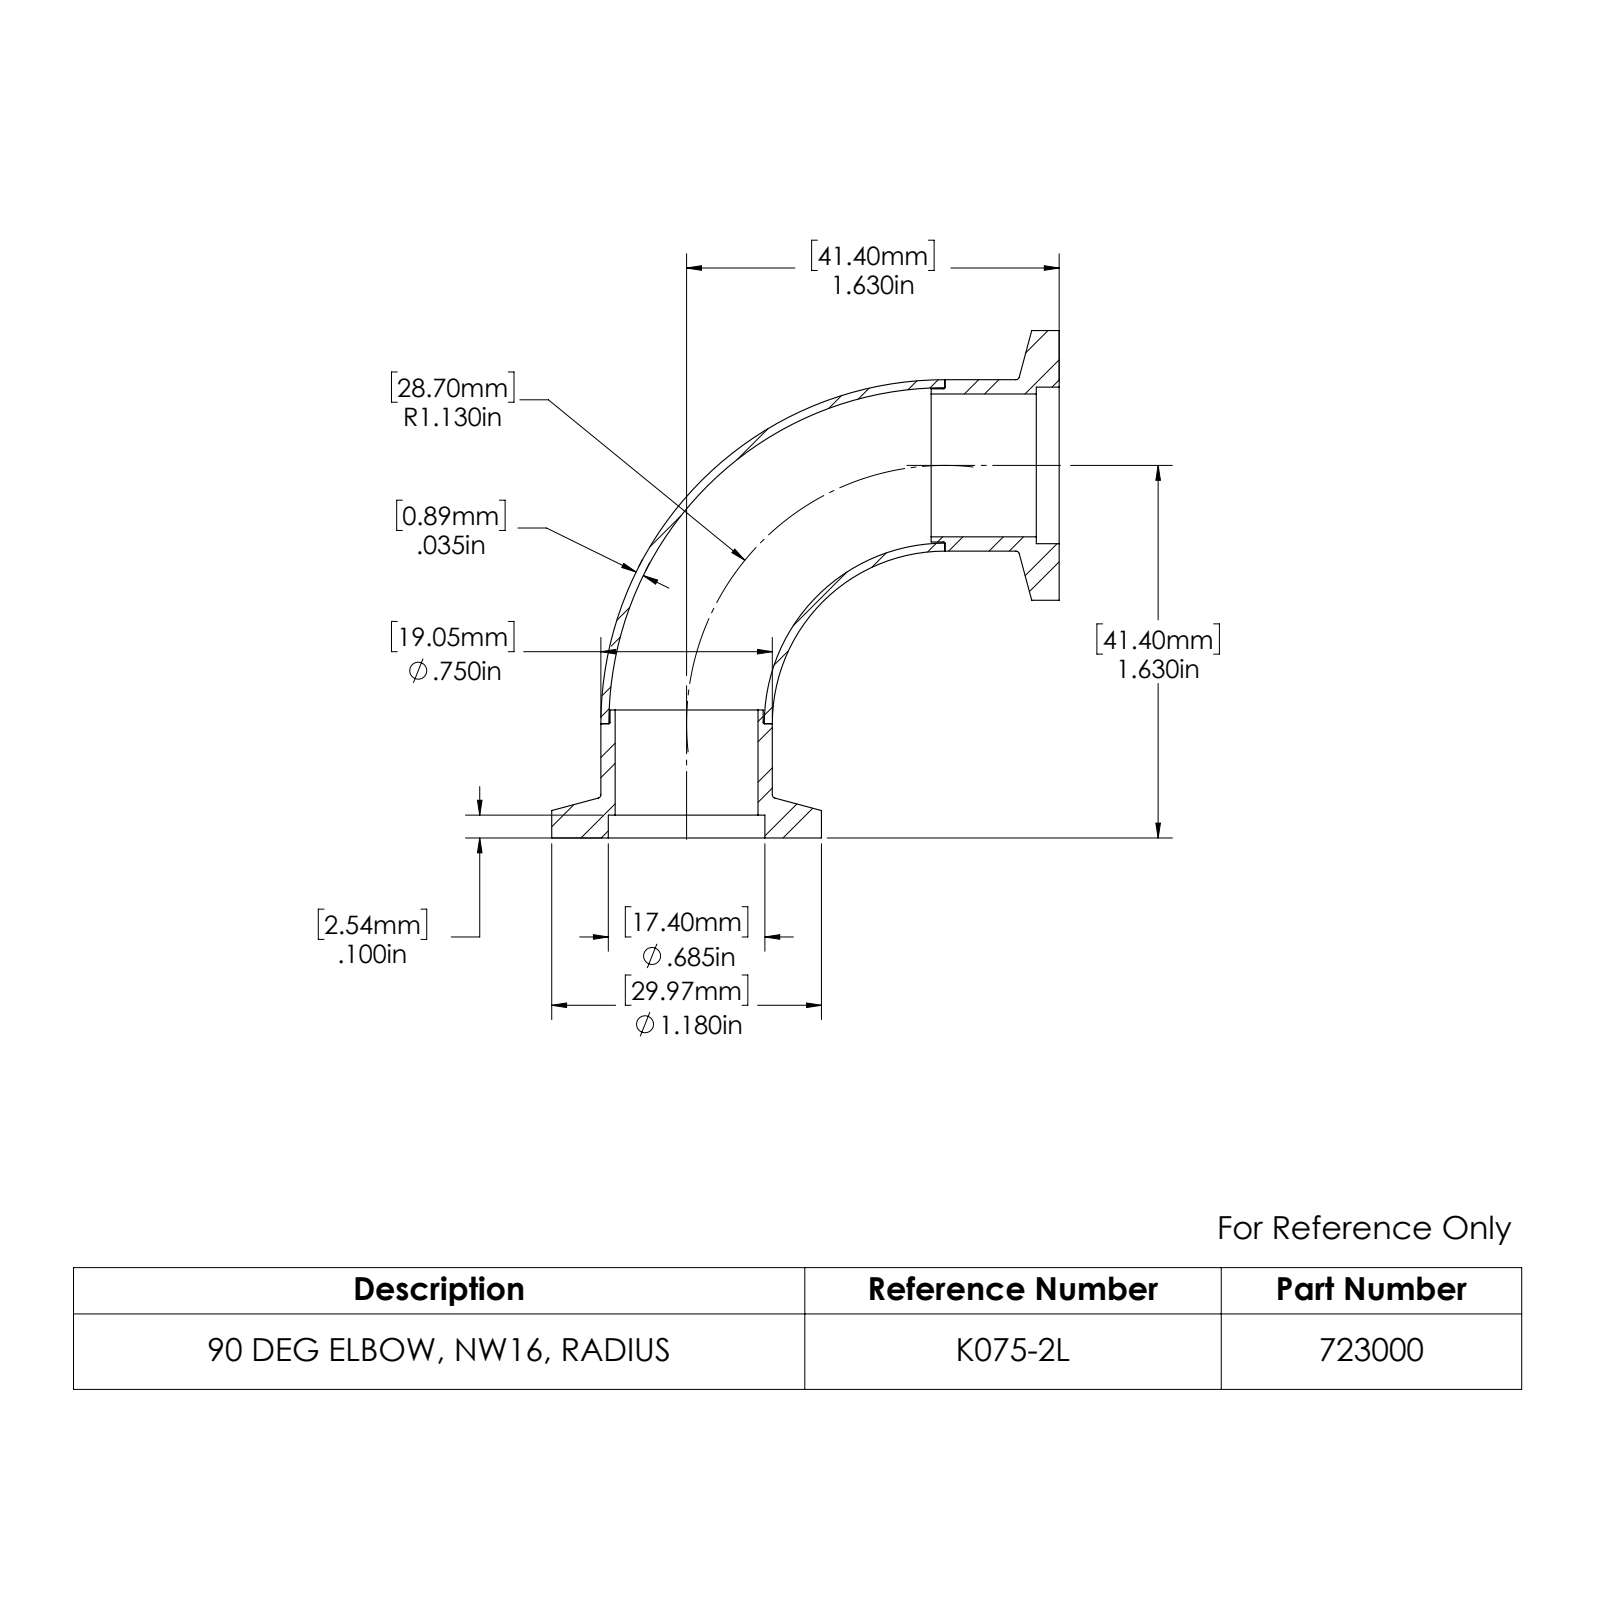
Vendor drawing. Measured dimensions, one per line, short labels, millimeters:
name: 403500; 713001; 723000-REV.D
written by: SolidWorks 2022 (AUTOMOTIVE_DESIGN)
unit: mm
bodies: 3 solids, 46 faces (10 planar, 20 cylindrical, 16 other)
size: 56.39 × 56.39 × 29.97
volume: 7 522 mm³; area: 10 450 mm²
holes: 2× ⌀15.88, 2× ⌀17.4
bosses: 2× ⌀29.97, 2× ⌀19.05, 2× ⌀17.02
face distances: 12.7, 2.54, 10.16, 14.23, 11.69, 1.53, 1.52, 11.68, 14.22
